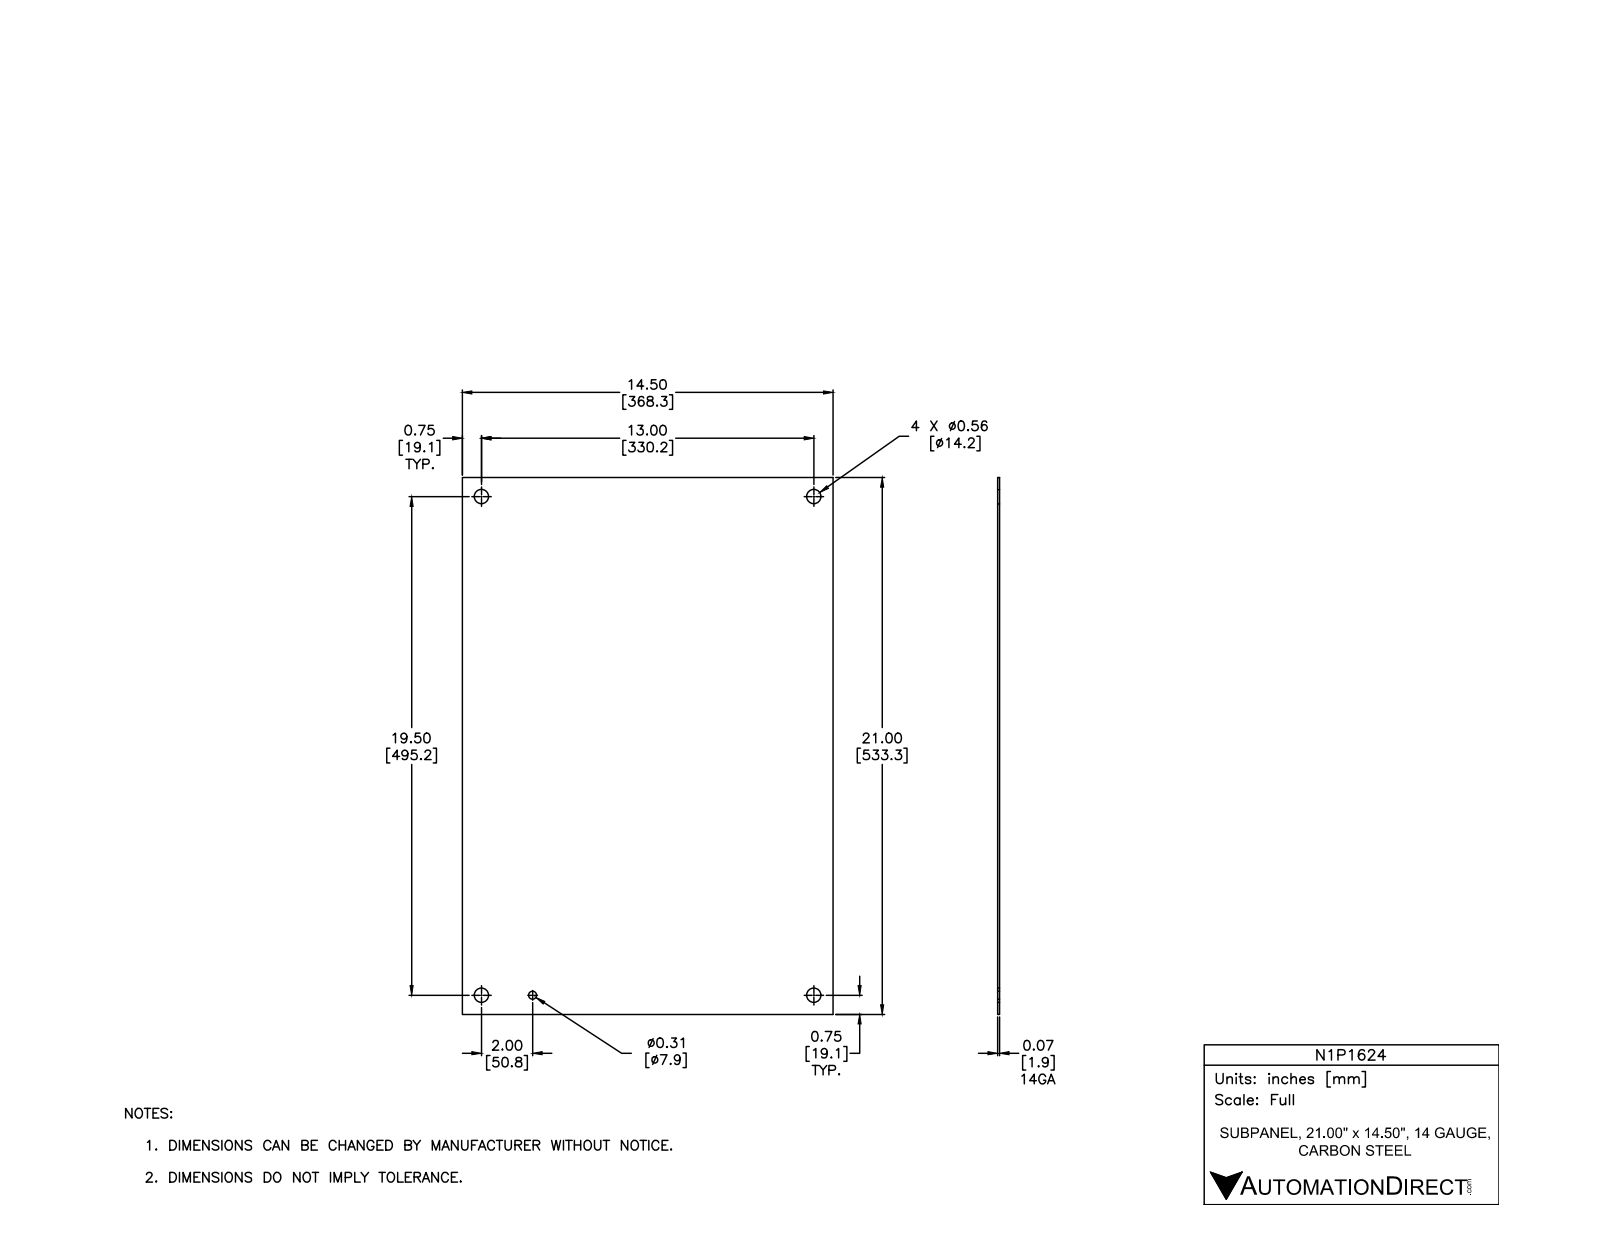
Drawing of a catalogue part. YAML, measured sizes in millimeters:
part_name: "N1P1624-1"
step_written_by: "Autodesk Inventor 2012 (AUTOMOTIVE_DESIGN)"
units: millimeters
bodies: {solids: 1, faces: 11, planar: 6, cylindrical: 5, other: 0}
overall_size: [533.4, 368.3, 1.9]
volume: 367900
surface_area: 395300
round_holes:
  - {diameter: 14.3, count: 4}
  - {diameter: 7.9, count: 1}
face_to_face_distances: [1.9, 368.3, 533.4]
hole_center_spacings: [330.2, 495.3, 595.3, 50.8, 279.4, 497.9, 568.7]
